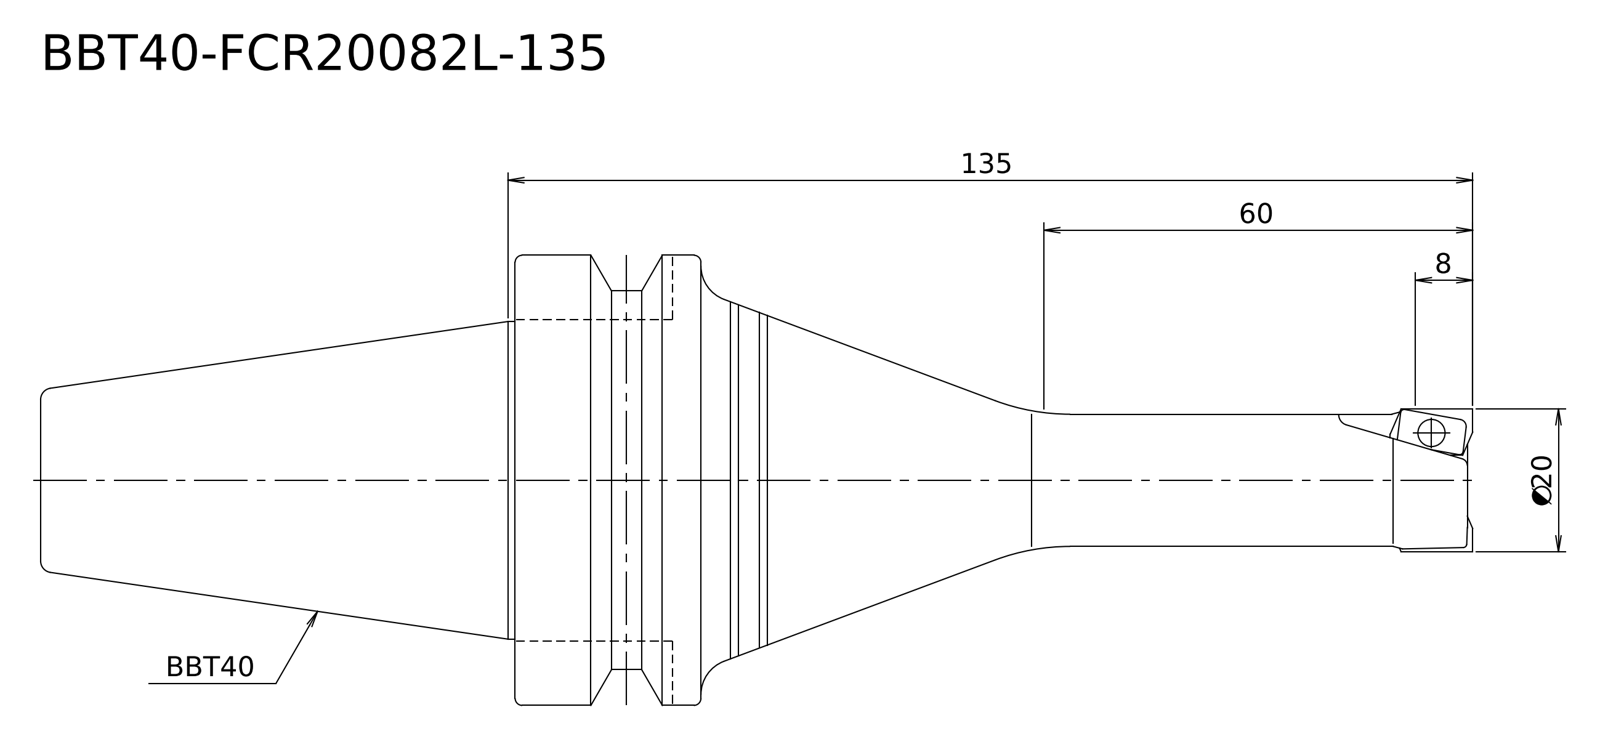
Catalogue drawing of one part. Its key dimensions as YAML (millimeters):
step_written_by: "Kubotek KeyCreator V8.5.1 (14335) (CONFIG_CONTROL_DESIGN)"
units: millimeters
bodies: {solids: 1, faces: 17, planar: 4, cylindrical: 6, other: 7}
overall_size: [200.4, 63, 63]
volume: 208647
surface_area: 25674
round_bosses_or_shafts:
  - {diameter: 63, count: 1}
  - {diameter: 53, count: 1}
  - {diameter: 44.45, count: 1}
  - {diameter: 20, count: 1}
  - {diameter: 18.5, count: 1}
face_to_face_distances: [66.4, 134, 200.4, 108, 26, 92.4]
